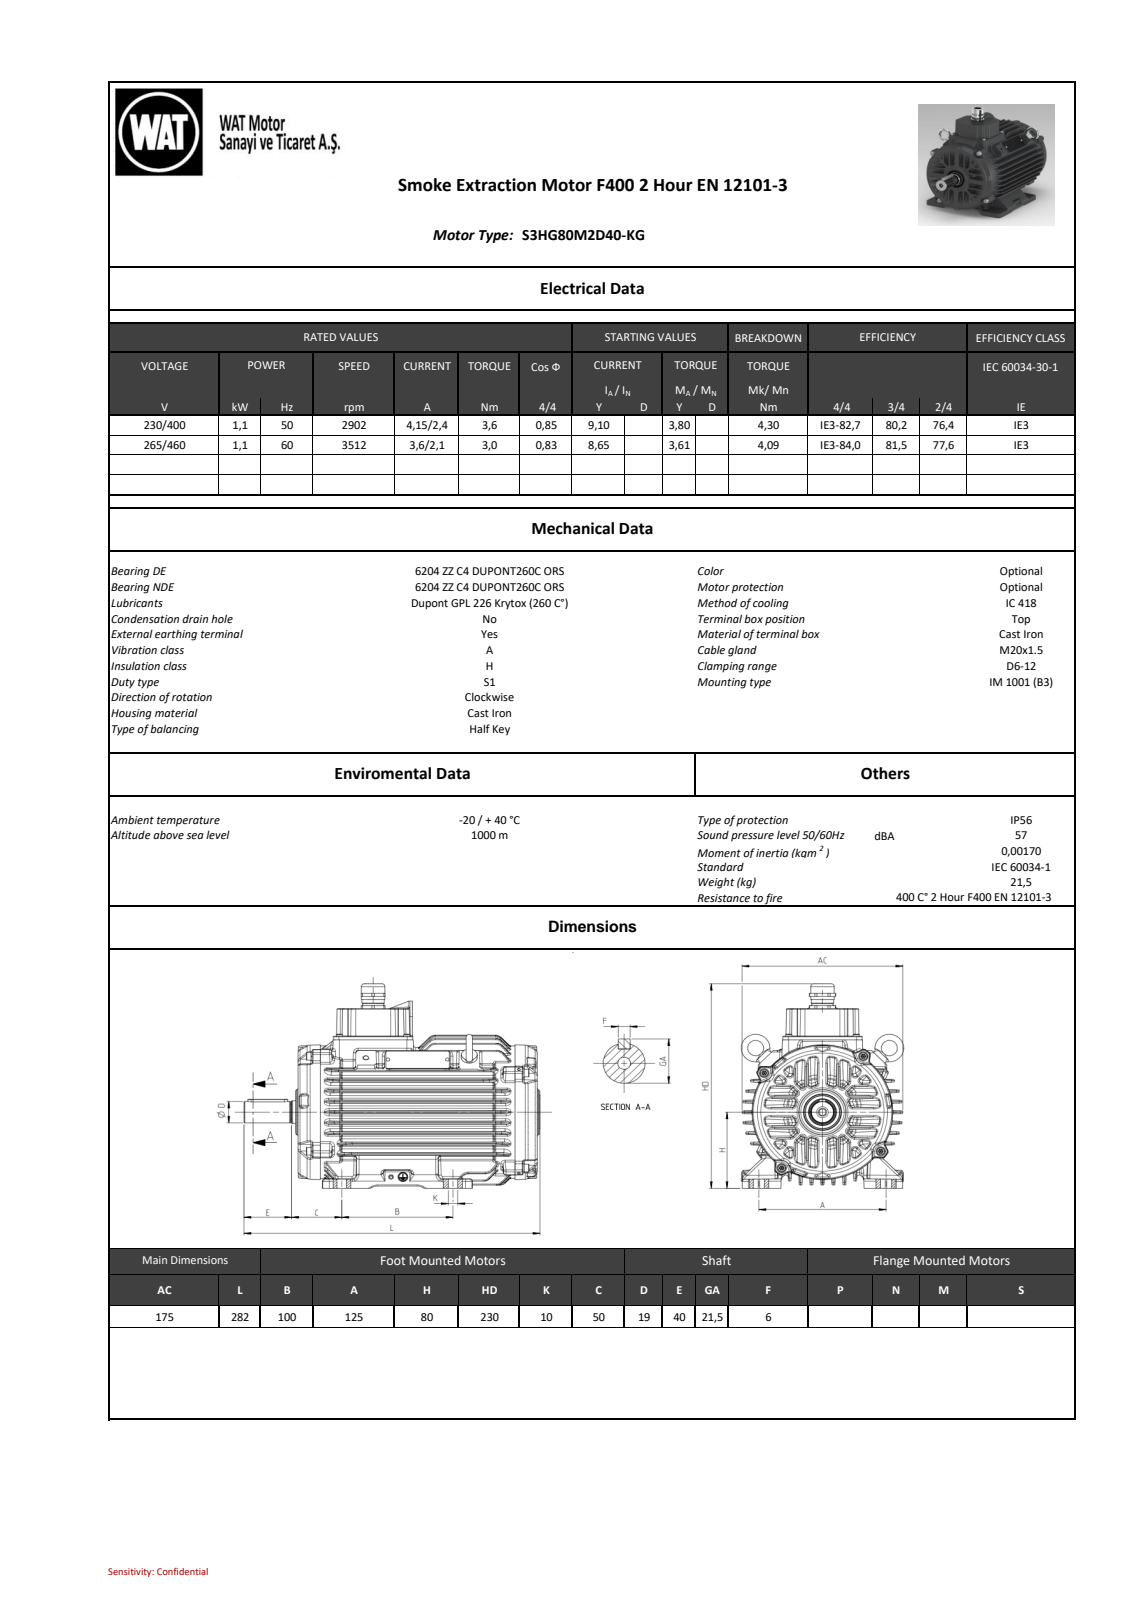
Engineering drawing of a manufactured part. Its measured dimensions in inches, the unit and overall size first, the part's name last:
Units: inches
Overall size (bounding box): 11.11 × 9.057 × 8.714
Round holes (diameter × count): ⌀0.13 ×6, ⌀0.098 ×2, ⌀0.165 ×2, ⌀0.252 ×1, ⌀0.551 ×1, ⌀0.945 ×1, ⌀1.094 ×1, ⌀1.102 ×1, ⌀1.26 ×1
Round bosses / shafts (diameter × count): ⌀0.315 ×4, ⌀0.787 ×3, ⌀0.362 ×3, ⌀0.326 ×3, ⌀0.197 ×3, ⌀0.933 ×1, ⌀0.882 ×1, ⌀0.829 ×1
Partial cylindrical surfaces — rounded edges, fillets, slot ends (radius × count): R0.059 ×384, R0.079 ×50, R0.098 ×50, R0.039 ×21, R0.02 ×19, R0.157 ×14, R0.197 ×10, R0.118 ×6
Main face-to-face distances: 8.97, 1.574, 6.022, 7.596, 9.167, 0.197, 0.03, 0.722, 8.248, 8.445
Hole centre spacings: 2.894, 0.038, 2.953, 5.012
Bodies: 0 solids, 2975 faces (577 planar, 750 cylindrical, 1648 other)
Part name (STEP PRODUCT): 26032C0836B7xhrx
STEP written by: SIEMENS PLM Software NX 11.0 (AUTOMOTIVE_DESIGN)
